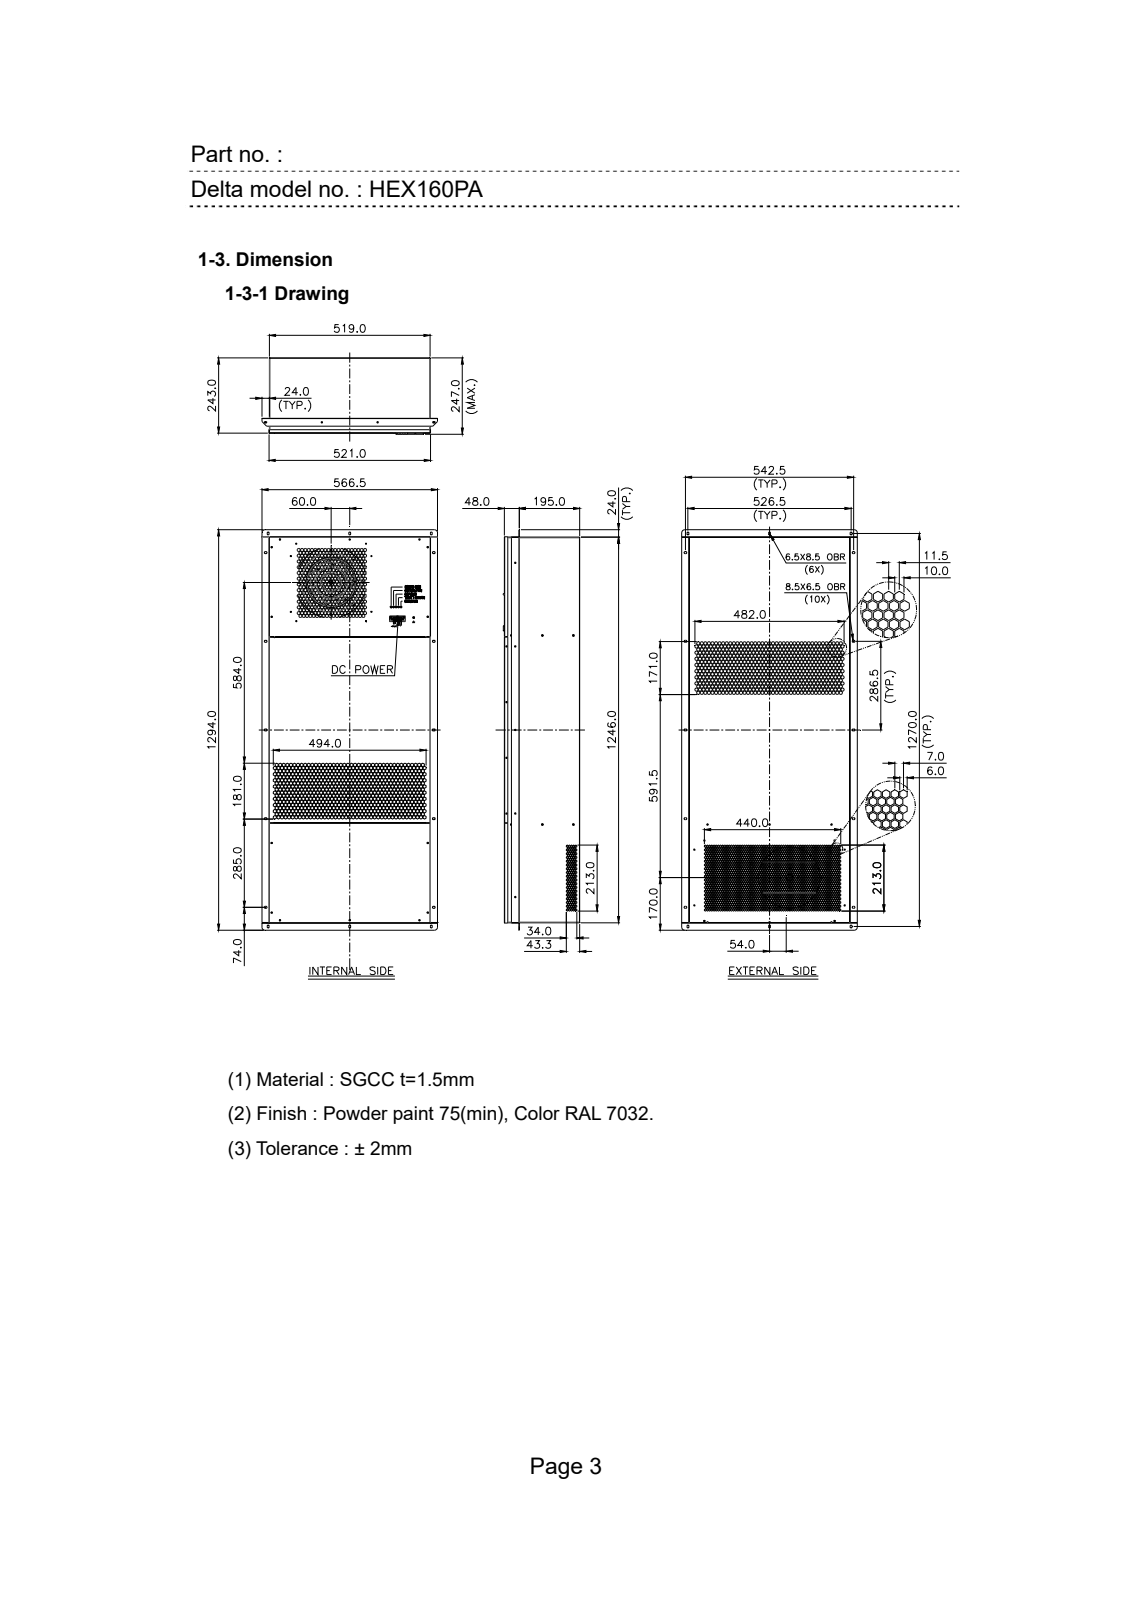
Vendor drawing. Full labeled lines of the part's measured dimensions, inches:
Part name (STEP PRODUCT): HEX160PA
STEP written by: SolidWorks 2011 (CONFIG_CONTROL_DESIGN)
Units: inches
Bodies: 1 solid, 135 faces (89 planar, 46 cylindrical, 0 other)
Overall size (bounding box): 50.945 × 22.303 × 9.882
Volume: 9 526 in³ · Surface area: 3 638 in²
Partial cylindrical surfaces — rounded edges, fillets, slot ends (radius × count): R0.128 ×32, R0.787 ×4
Main face-to-face distances: 9.567, 0.157, 9.409, 20.413, 0.079, 9.252, 49.055, 7.677, 7.52, 1.732
